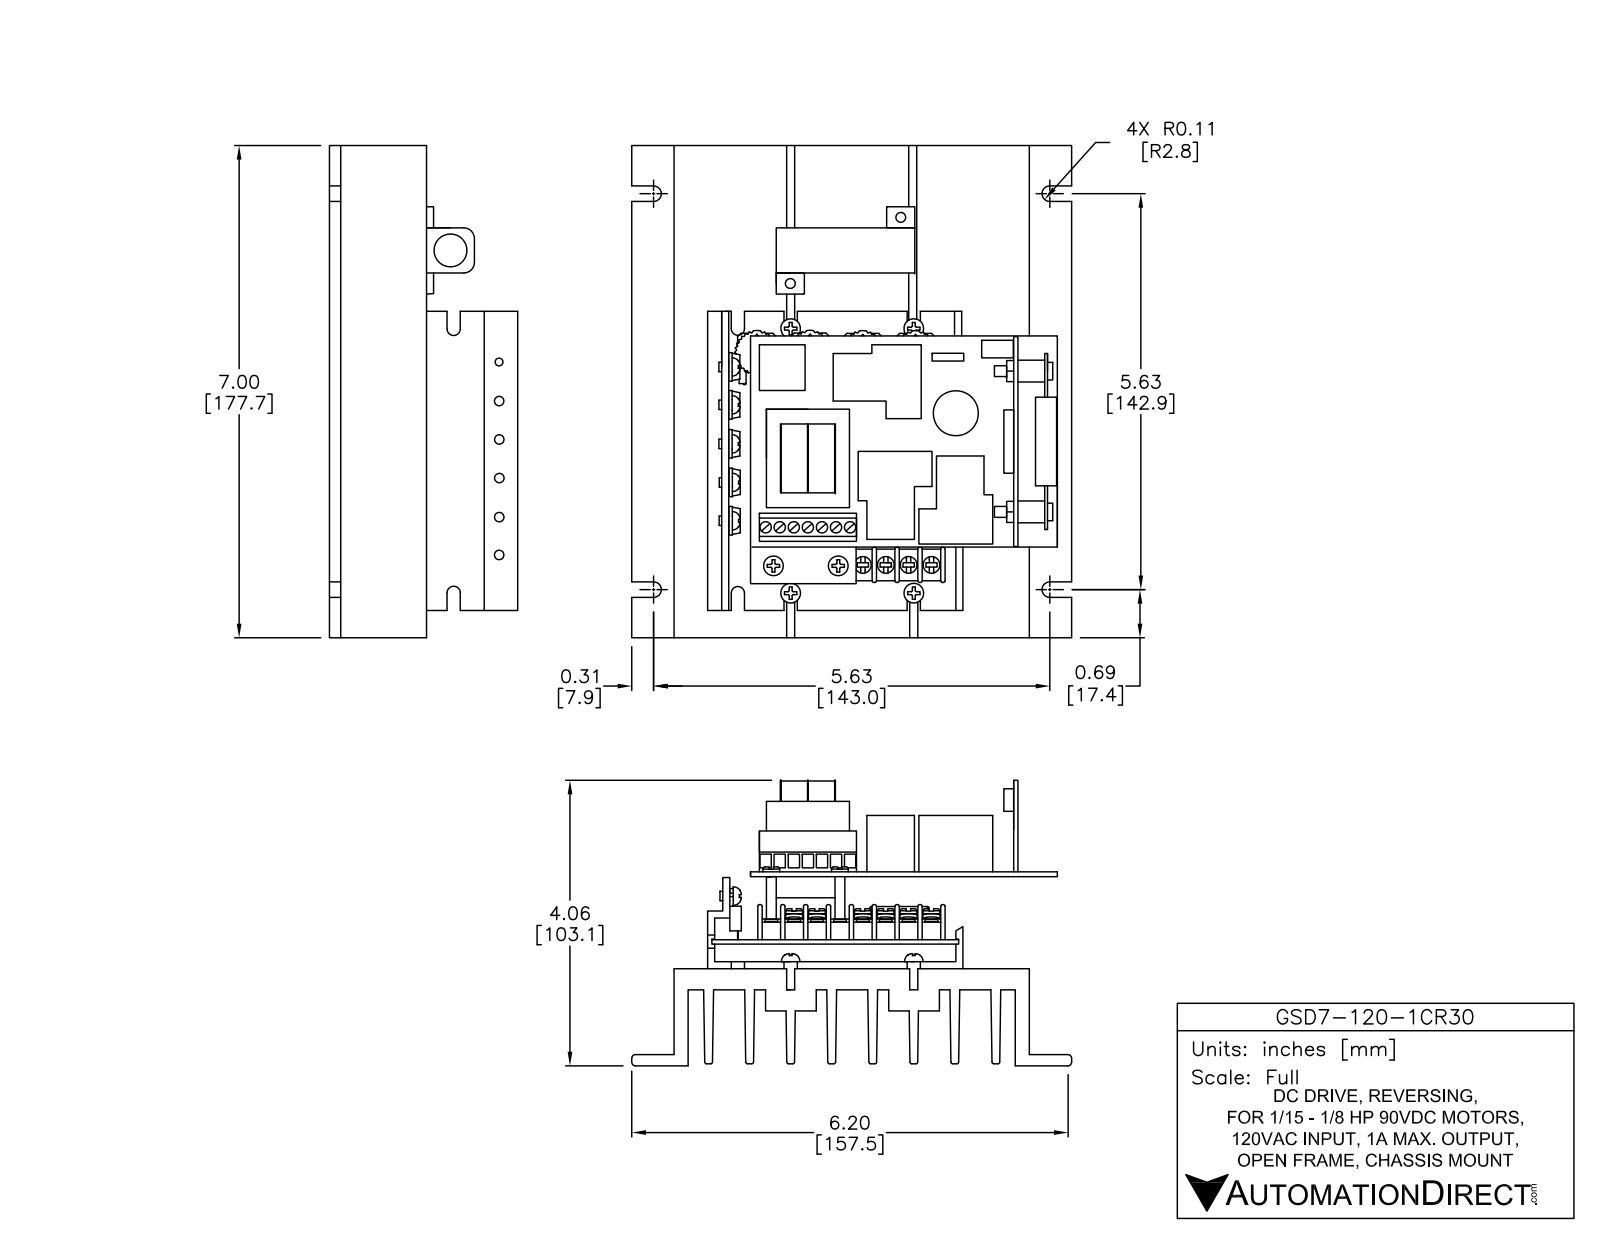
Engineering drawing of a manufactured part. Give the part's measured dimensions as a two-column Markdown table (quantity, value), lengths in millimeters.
| quantity | value |
| --- | --- |
| part name | Q59; 125-Assembly; TH_CAP_AXIAL_20S-16L-8D-8.2H; R24 (+8 more) |
| STEP written by | SolidWorks 2014 (AUTOMOTIVE_DESIGN) |
| units | millimeters |
| bodies | 106 solids, 5609 faces (3006 planar, 1961 cylindrical, 642 other) |
| overall size | 177.8 × 159.9 × 99.1 |
| volume | 565 400 mm³ |
| surface area | 301 100 mm² |
| round holes (diameter × count) | 0.8 × 90, 1.1 × 19, 0.9 × 16, 1.2 × 12, 1.8 × 9, 0.9 × 8, 2.3 × 7, 3.7 × 7, 1 × 6, 2.8 × 6, 3.7 × 5, 2.8 × 4 |
| round bosses / shafts (diameter × count) | 0.6 × 43, 0.6 × 30, 0.6 × 22, 2.7 × 20, 2.1 × 20, 2 × 19, 0.8 × 16, 0.5 × 12 |
| partial cylindrical surfaces (radius × count) | 0.3 × 25, 0.1 × 23, 0.5 × 12, 1.6 × 12, 1 × 11, 0.6 × 10, 1.1 × 8, 2.4 × 8 |
| main face-to-face distances | 14.9, 29.7, 59.3, 44.5, 7.6, 74.2, 89, 44.6, 2.5, 29.6 |
| hole center spacings | 5.1, 14, 2.5, 10.2, 11.7, 16.2, 19.1, 20.3 |
